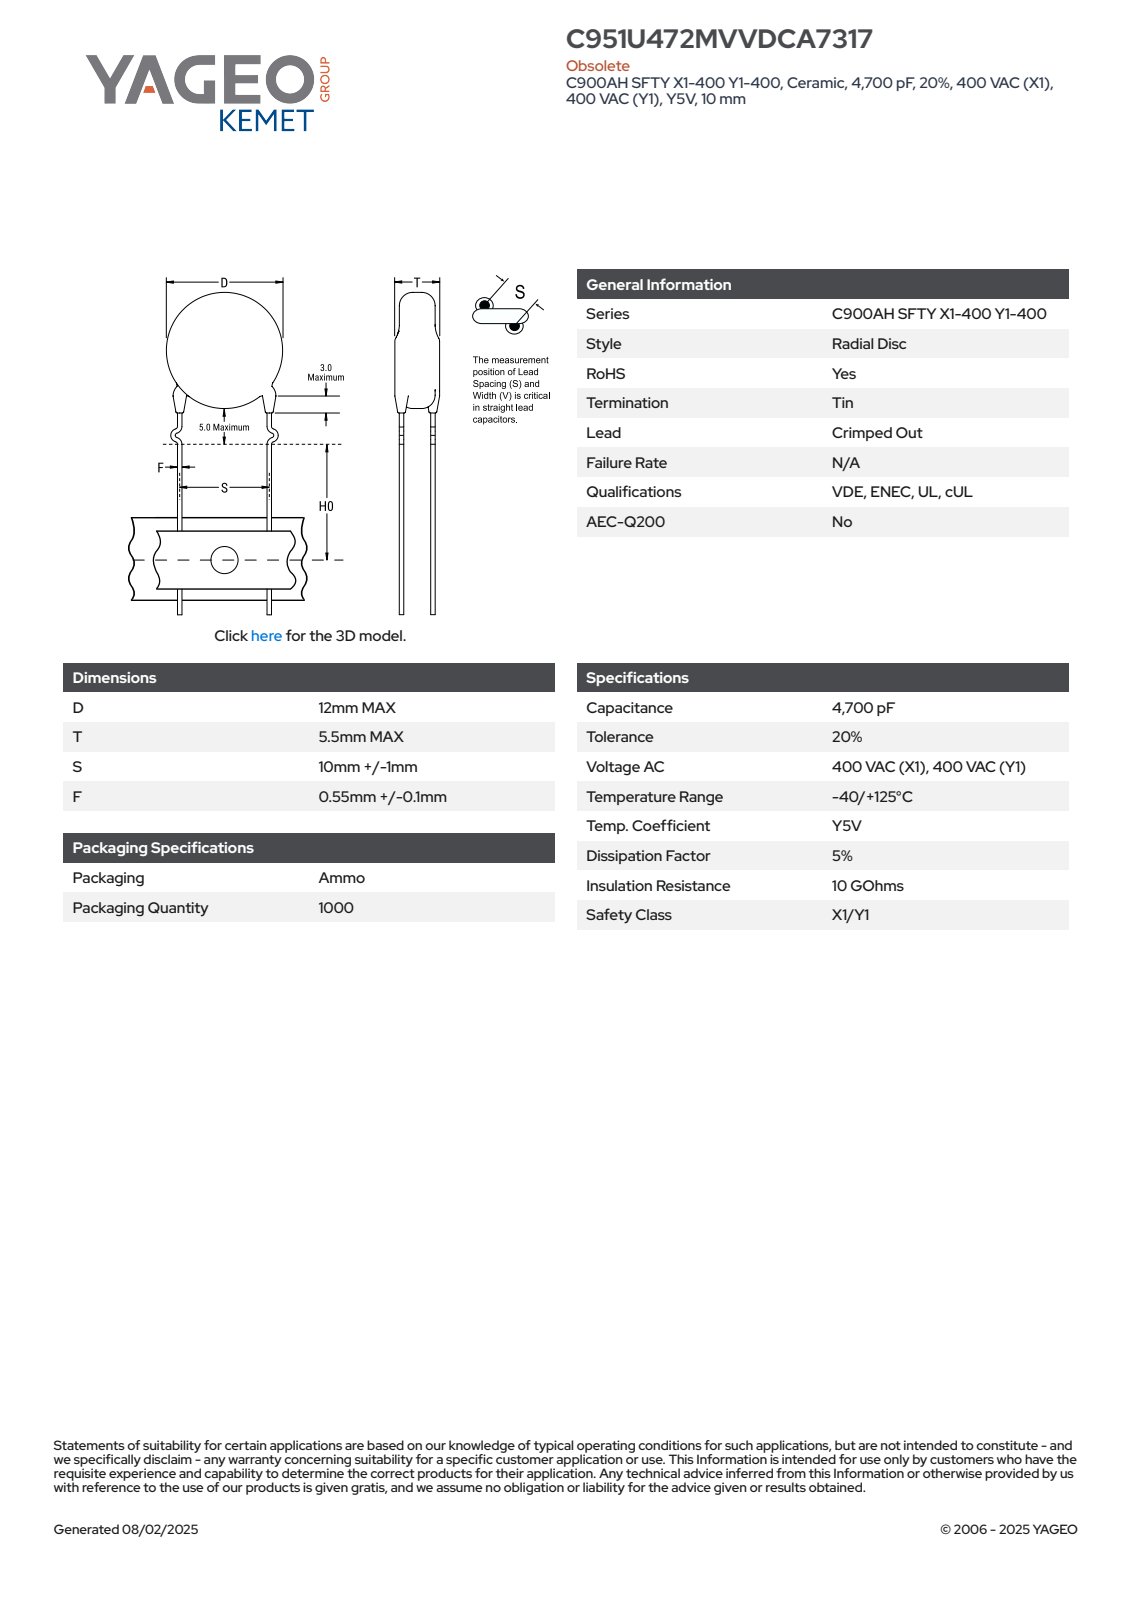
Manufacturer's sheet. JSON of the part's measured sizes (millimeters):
{"part_name": "CCD_KCOC900_D12T5.5S10LL20F0.55", "step_written_by": "SolidWorks 2014 (AUTOMOTIVE_DESIGN)", "units": "millimeters", "bodies": {"solids": 4, "faces": 85, "planar": 63, "cylindrical": 6, "other": 16}, "overall_size": [37, 14.84, 5.5], "volume_mm3": 630, "surface_area_mm2": 539, "round_bosses_or_shafts": [[1.2, 2], [12, 1]], "face_to_face_distances": [5.5, 6.63, 5.39, 1.24, 0.34, 5.1, 0.46, 1, 0.45, 2.58]}
